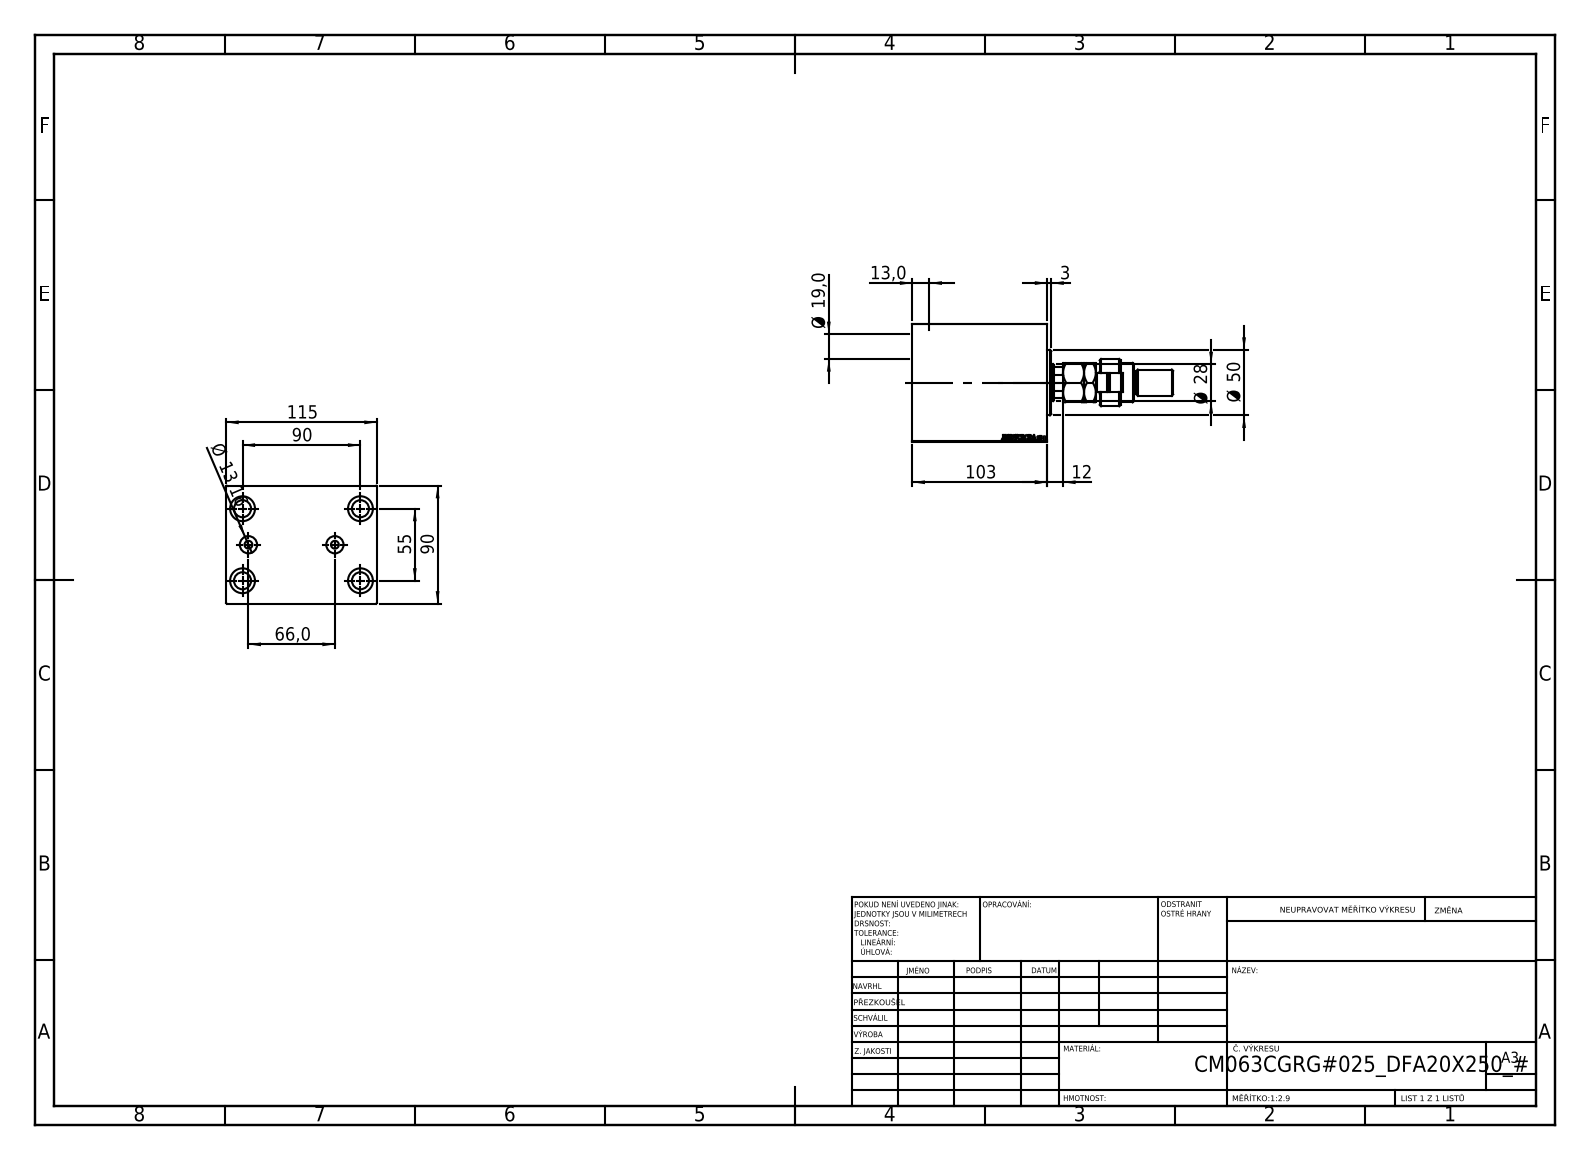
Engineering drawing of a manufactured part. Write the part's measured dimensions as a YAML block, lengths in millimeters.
part_name: "V450CM_C_Body; V450CM_VC_B; V450CM_C_VCP; MFA (+1 more)"
step_written_by: "SolidWorks 2019 (CONFIG_CONTROL_DESIGN)"
units: millimeters
bodies: {solids: 5, faces: 945, planar: 436, cylindrical: 71, other: 438}
overall_size: [199, 115, 90]
volume: 1016000
surface_area: 136676
round_holes:
  - {diameter: 13, count: 4}
  - {diameter: 19, count: 4}
  - {diameter: 6, count: 2}
  - {diameter: 13.16, count: 2}
  - {diameter: 18.5, count: 1}
  - {diameter: 28, count: 1}
  - {diameter: 31.5, count: 1}
  - {diameter: 63, count: 1}
  - {diameter: 65, count: 1}
  - {diameter: 72, count: 1}
round_bosses_or_shafts:
  - {diameter: 50, count: 1}
  - {diameter: 36, count: 1}
  - {diameter: 30, count: 1}
  - {diameter: 22, count: 1}
  - {diameter: 20, count: 1}
  - {diameter: 18, count: 1}
  - {diameter: 14, count: 1}
partial_cylinders:
  - {radius: 7.5, count: 1}
  - {radius: 12, count: 1}
  - {radius: 13.5, count: 1}
face_to_face_distances: [90, 115, 103, 52, 51, 10, 21.6, 29.4, 81.4, 71.4]
hole_center_spacings: [52.74, 27.87, 33.71, 55, 75.67, 89.81, 90, 105.48]
